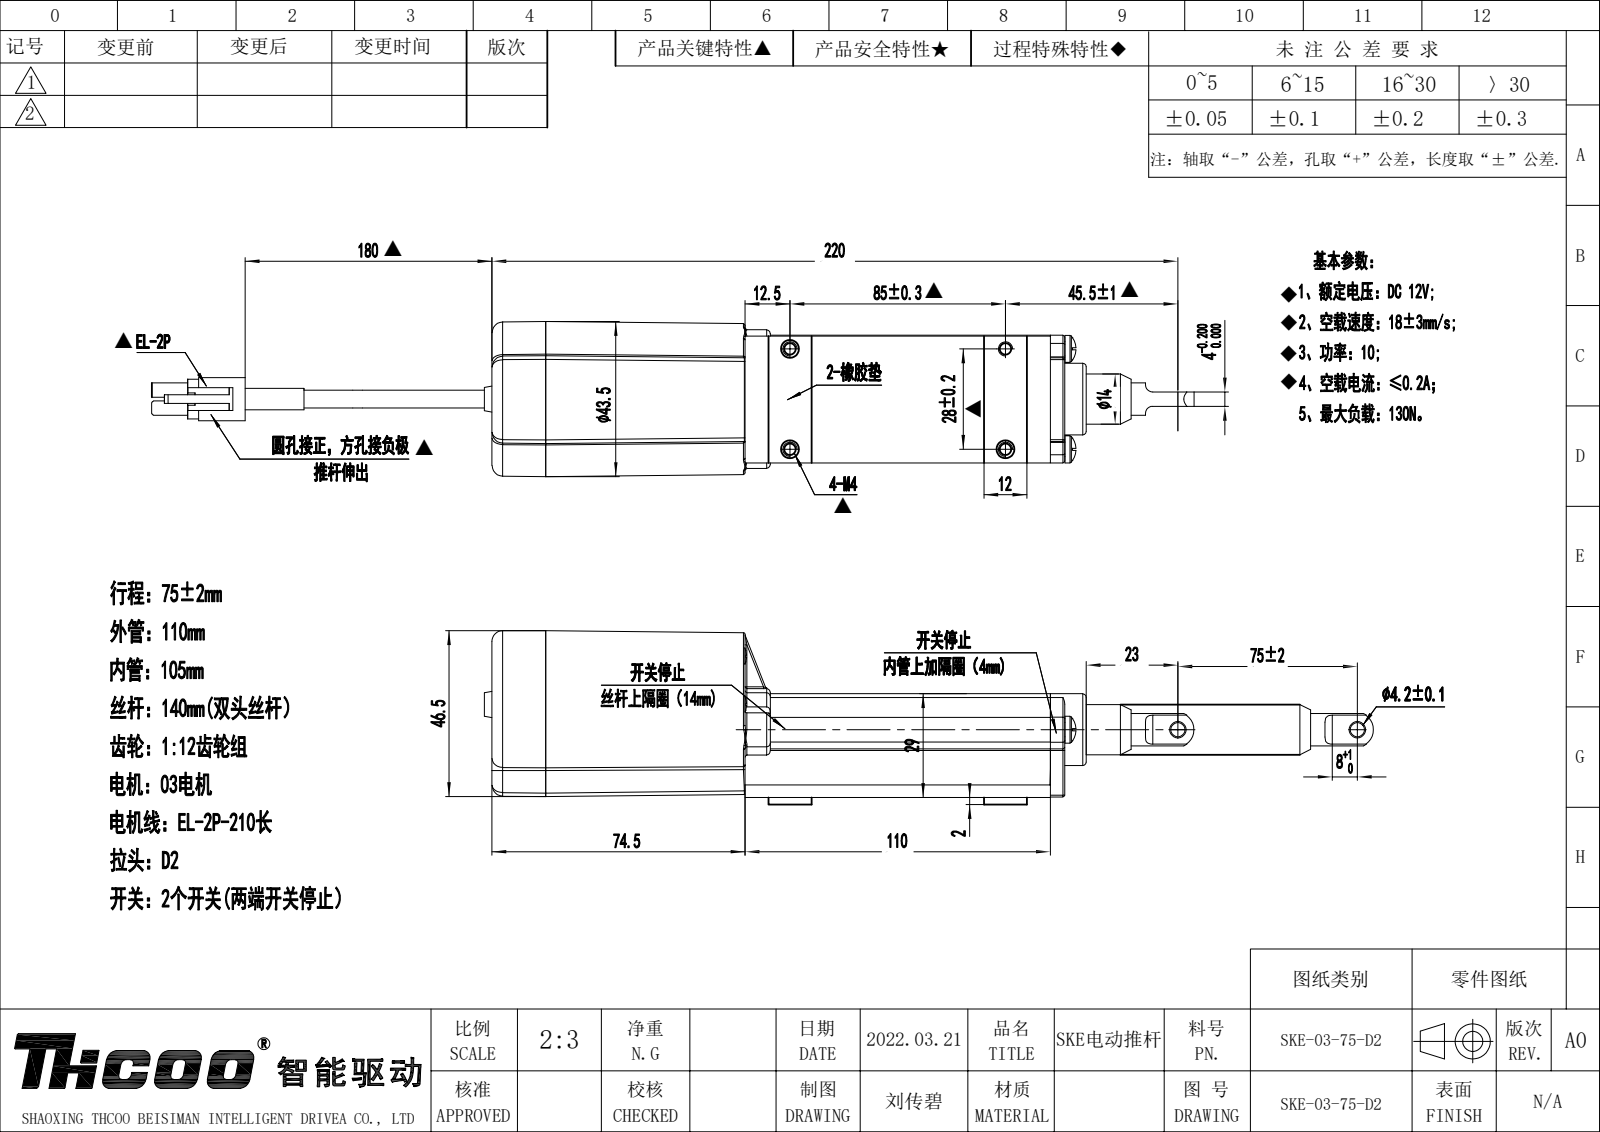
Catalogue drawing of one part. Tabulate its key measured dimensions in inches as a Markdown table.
| quantity | value |
| --- | --- |
| part name | Admi0CB42C5Fkiav |
| STEP written by | SIEMENS PLM Software NX 12.0 (AUTOMOTIVE_DESIGN) |
| units | inches |
| bodies | 8 solids, 773 faces (321 planar, 248 cylindrical, 204 other) |
| overall size | 11.619 × 1.908 × 1.703 |
| volume | 6.241 in³ |
| surface area | 141.7 in² |
| round holes (diameter × count) | 0.157 × 4, 0.189 × 4, 0.126 × 3, 0.165 × 3, 0.197 × 3, 0.248 × 1, 0.276 × 1, 0.323 × 1, 0.394 × 1, 0.559 × 1, 0.63 × 1 |
| round bosses / shafts (diameter × count) | 0.295 × 2, 0.157 × 2, 0.787 × 1, 0.626 × 1, 0.591 × 1, 0.551 × 1, 0.472 × 1, 0.354 × 1 |
| partial cylindrical surfaces (radius × count) | 0.02 × 97, 0.039 × 19, 0.008 × 8, 0.016 × 7, 0.079 × 6, 0.118 × 6, 0.043 × 4, 0.071 × 4 |
| main face-to-face distances | 0.079, 0.839, 0.059, 0.098, 0.157, 0.138, 0.236, 0.917, 0.315, 0.787 |
| hole center spacings | 1.102, 0.282, 0.551, 0.67, 1.194, 3.74, 3.899, 0.611 |
